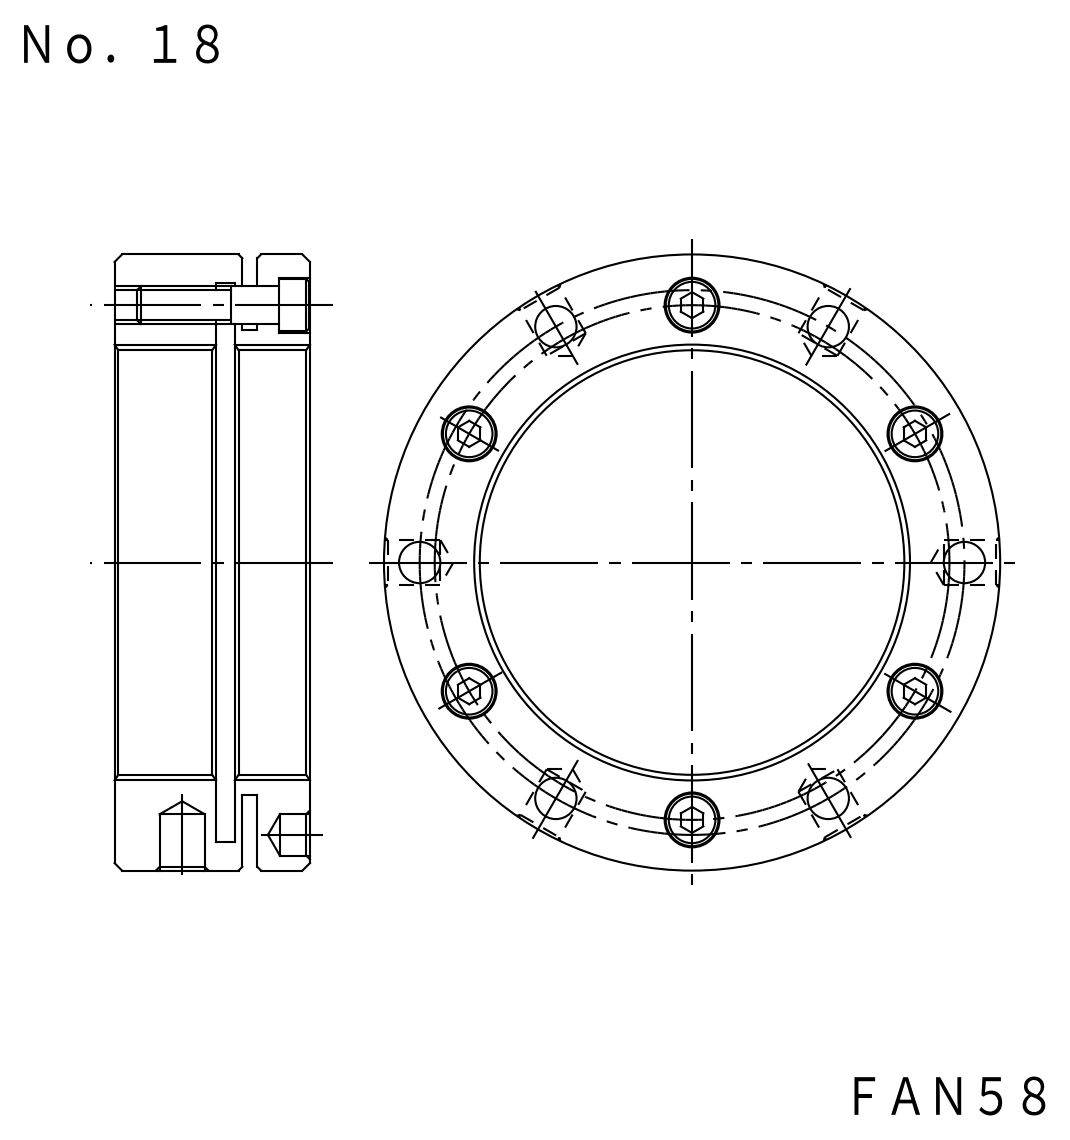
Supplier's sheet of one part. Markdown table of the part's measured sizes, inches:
| quantity | value |
| --- | --- |
| part name | FKD FAN58; M5X18_default |
| STEP written by | SolidWorks 2012 (CONFIG_CONTROL_DESIGN) |
| units | inches |
| bodies | 7 solids, 204 faces (72 planar, 108 cylindrical, 24 other) |
| overall size | 3.228 × 3.228 × 1.024 |
| volume | 3.47 in³ |
| surface area | 47.77 in² |
| round holes (diameter × count) | 0.163 × 6, 0.209 × 6, 0.217 × 6, 0.354 × 6, 0.236 × 3, 2.283 × 1, 2.992 × 1 |
| round bosses / shafts (diameter × count) | 0.335 × 6, 0.197 × 6, 3.228 × 1, 2.52 × 1 |
| main face-to-face distances | 0.098, 0.157, 1.024, 0.642, 0.382, 0.74, 0.283, 0.484, 0.256, 0.539 |
| hole center spacings | 1.378, 2.709, 1.984, 1.427, 0.728, 2.387, 1.427, 1.983 |
